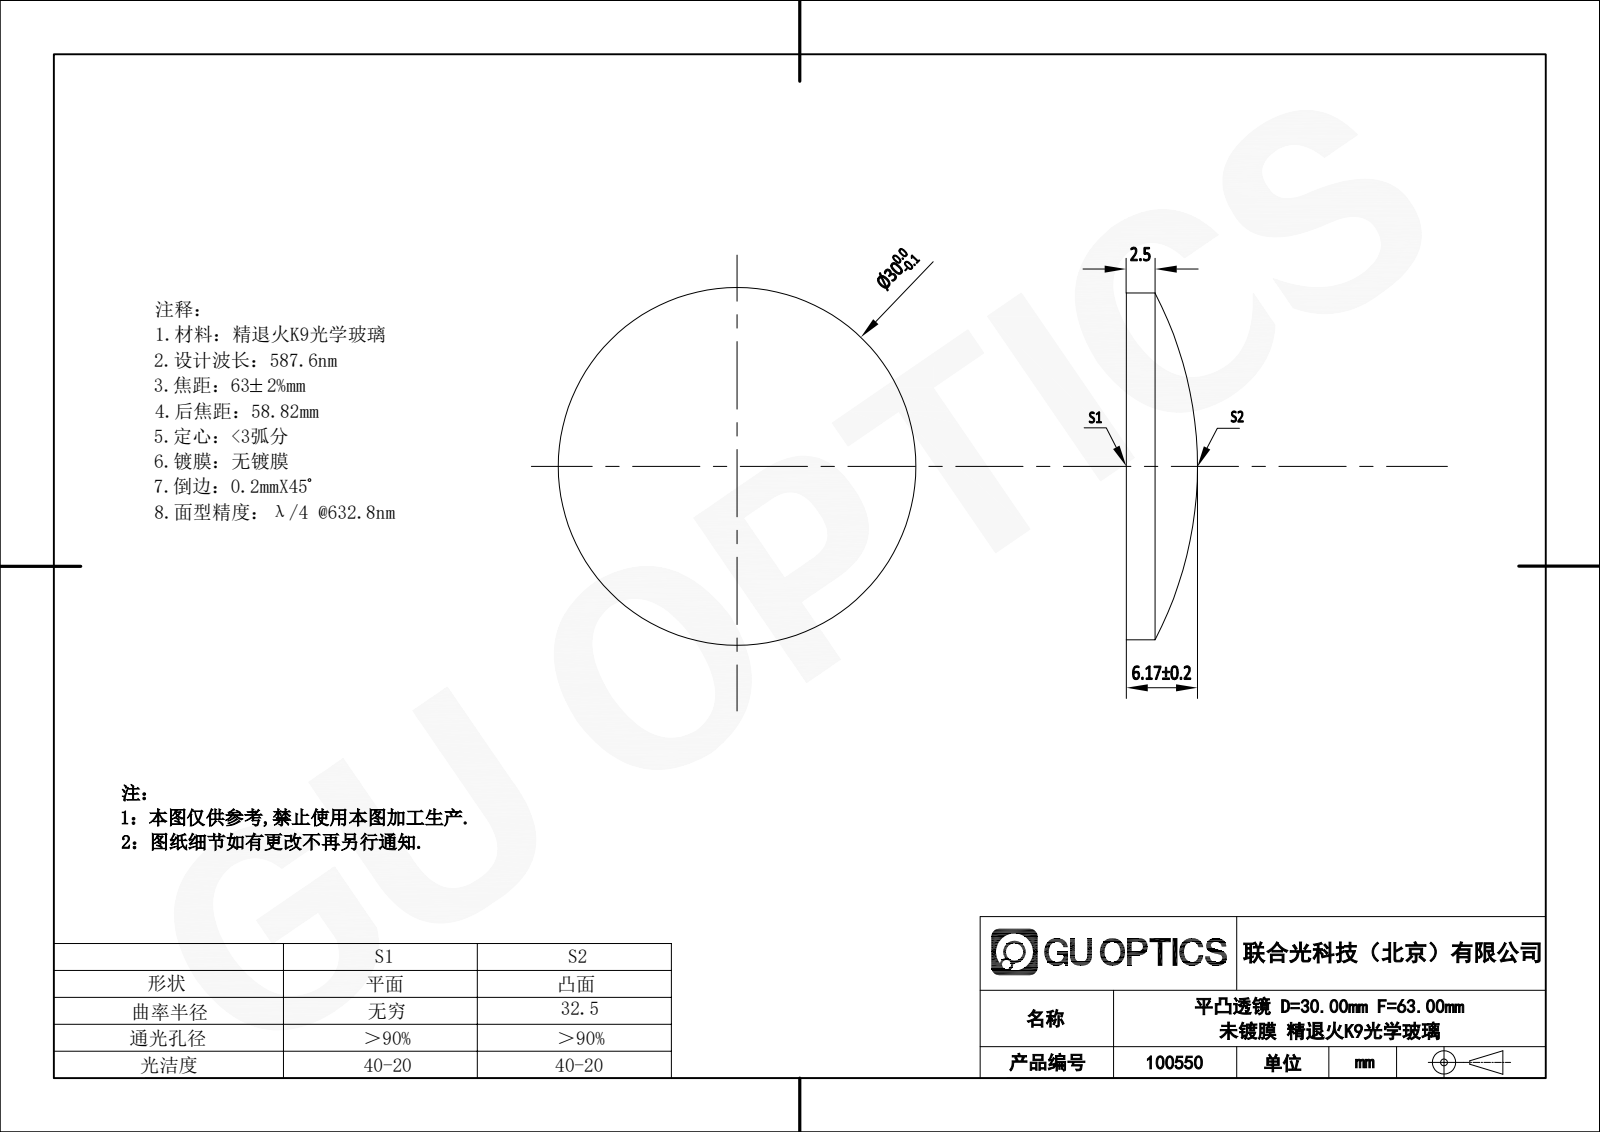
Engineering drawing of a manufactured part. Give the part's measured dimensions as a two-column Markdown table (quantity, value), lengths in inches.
| quantity | value |
| --- | --- |
| part name | 100550 |
| STEP written by | SolidWorks 2020 (CONFIG_CONTROL_DESIGN) |
| units | inches |
| bodies | 1 solid, 5 faces (1 planar, 2 cylindrical, 2 other) |
| overall size | 1.181 × 1.181 × 0.243 |
| volume | 0.189 in³ |
| surface area | 2.623 in² |
| round bosses / shafts (diameter × count) | 1.181 × 1 |
